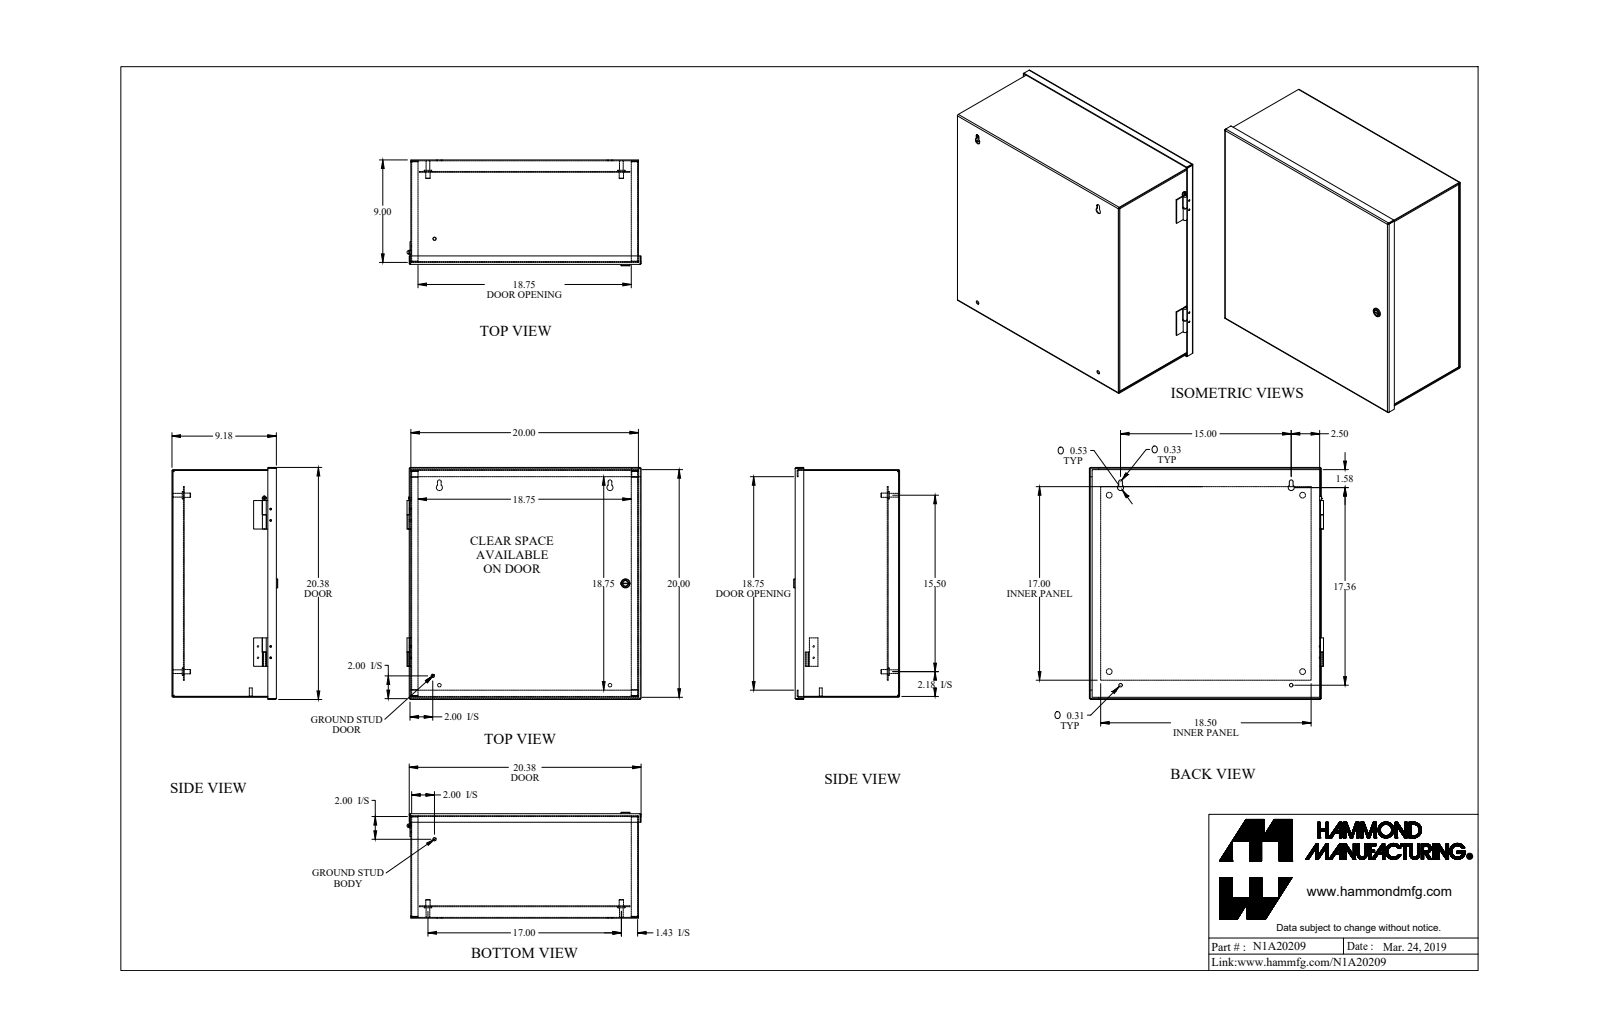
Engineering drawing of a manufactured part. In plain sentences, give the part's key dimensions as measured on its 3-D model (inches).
The part is named "N1A20209". Its 3-D file was written by "SolidWorks 2018 (AUTOMOTIVE_DESIGN)". It is 23 solids with 520 faces: 294 planar, 182 cylindrical and 44 other. Overall it measures 20.574 by 20.384 by 9.299 inches. Its volume is 144.3 cubic inches and its surface area 4 021 square inches. Round holes: 8 of diameter 0.14, 4 of diameter 0.5, 2 of diameter 0.307, 2 of diameter 0.312, 2 of diameter 0.445, 1 of diameter 0.17, 1 of diameter 0.187, 1 of diameter 0.516. Round bosses or shafts: 8 of diameter 0.128, 5 of diameter 0.375, 4 of diameter 0.65, 4 of diameter 0.33, 2 of diameter 1, 2 of diameter 0.281, 2 of diameter 0.25, 1 of diameter 0.788. Partial cylindrical surfaces (rounded edges, fillets, slot ends): 16 of radius 0.036, 16 of radius 0.108, 2 of radius 0.06, 2 of radius 0.153, 2 of radius 0.164, 2 of radius 0.266, 1 of radius 0.03, 1 of radius 0.125. The main face-to-face distances are 0.072, 9.105, 19.928, 1.009, 8.096, 9.033, 9.177, 20, 19.856, 1.081. The hole center spacings are 1, 1.119, 1.553, 2.031, 7.758, 12.062, 12.062, 12.113.
